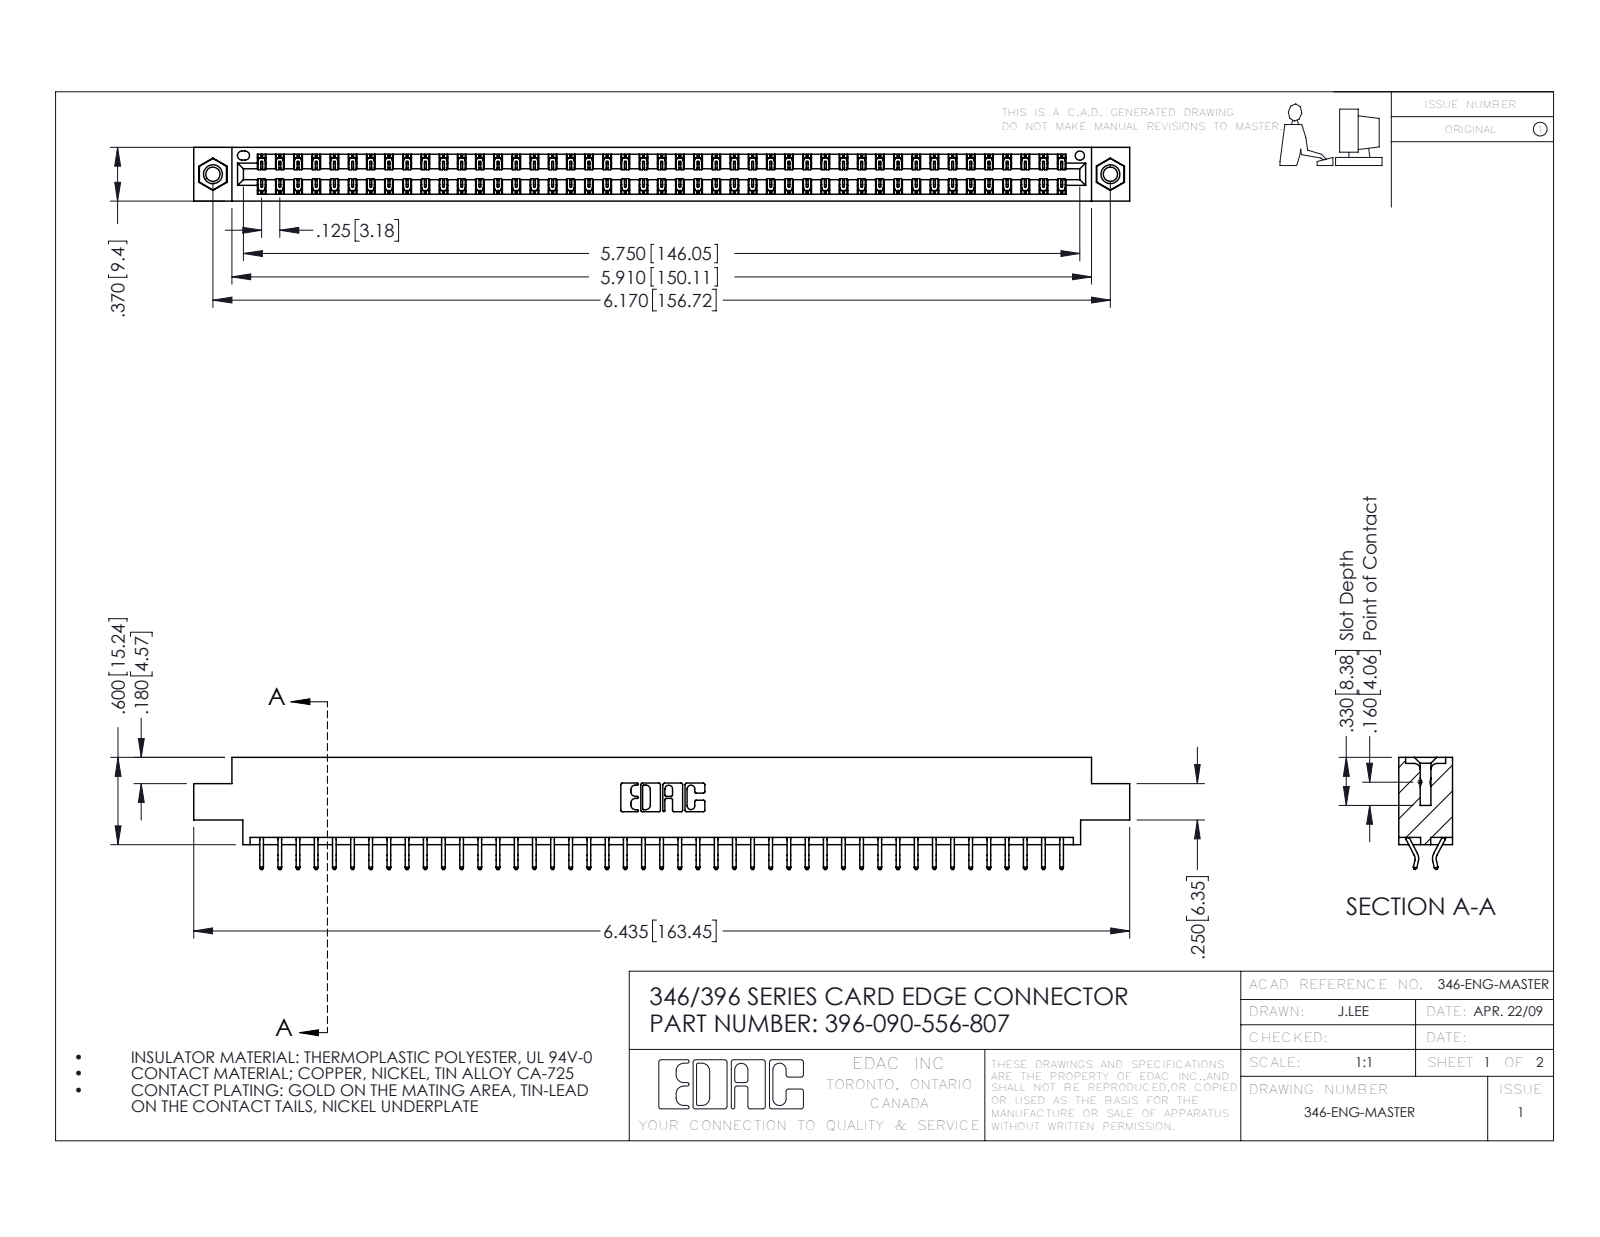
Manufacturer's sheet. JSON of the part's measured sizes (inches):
{"part_name": "345-292-001_556 Tail; 346 Part_0.170 Offset - 0.156 Dia-TI; 345-250-001_345-250-005-103; 396-090-556-807", "step_written_by": "SolidWorks 2016 (CONFIG_CONTROL_DESIGN)", "units": "inches", "bodies": {"solids": 93, "faces": 5406, "planar": 3622, "cylindrical": 1768, "other": 16}, "overall_size": [6.435, 0.77, 0.37], "volume_in3": 0.964, "surface_area_in2": 33.92, "round_holes": [[0.098, 2], [0.125, 2], [0.156, 2], [0.064, 1]], "round_bosses_or_shafts": [[0.155, 2]], "partial_cylinders_radius": [[0.006, 135], [0.01, 22], [0.007, 6], [0.031, 6], [0.026, 3], [0.01, 2], [0.014, 2], [0.022, 2]], "face_to_face_distances": [0.048, 0.322, 0.37, 0.25, 0.025, 0.072, 0.298, 0.275, 0.222, 0.148], "hole_center_spacings": [0.246, 5.961, 6.17]}
